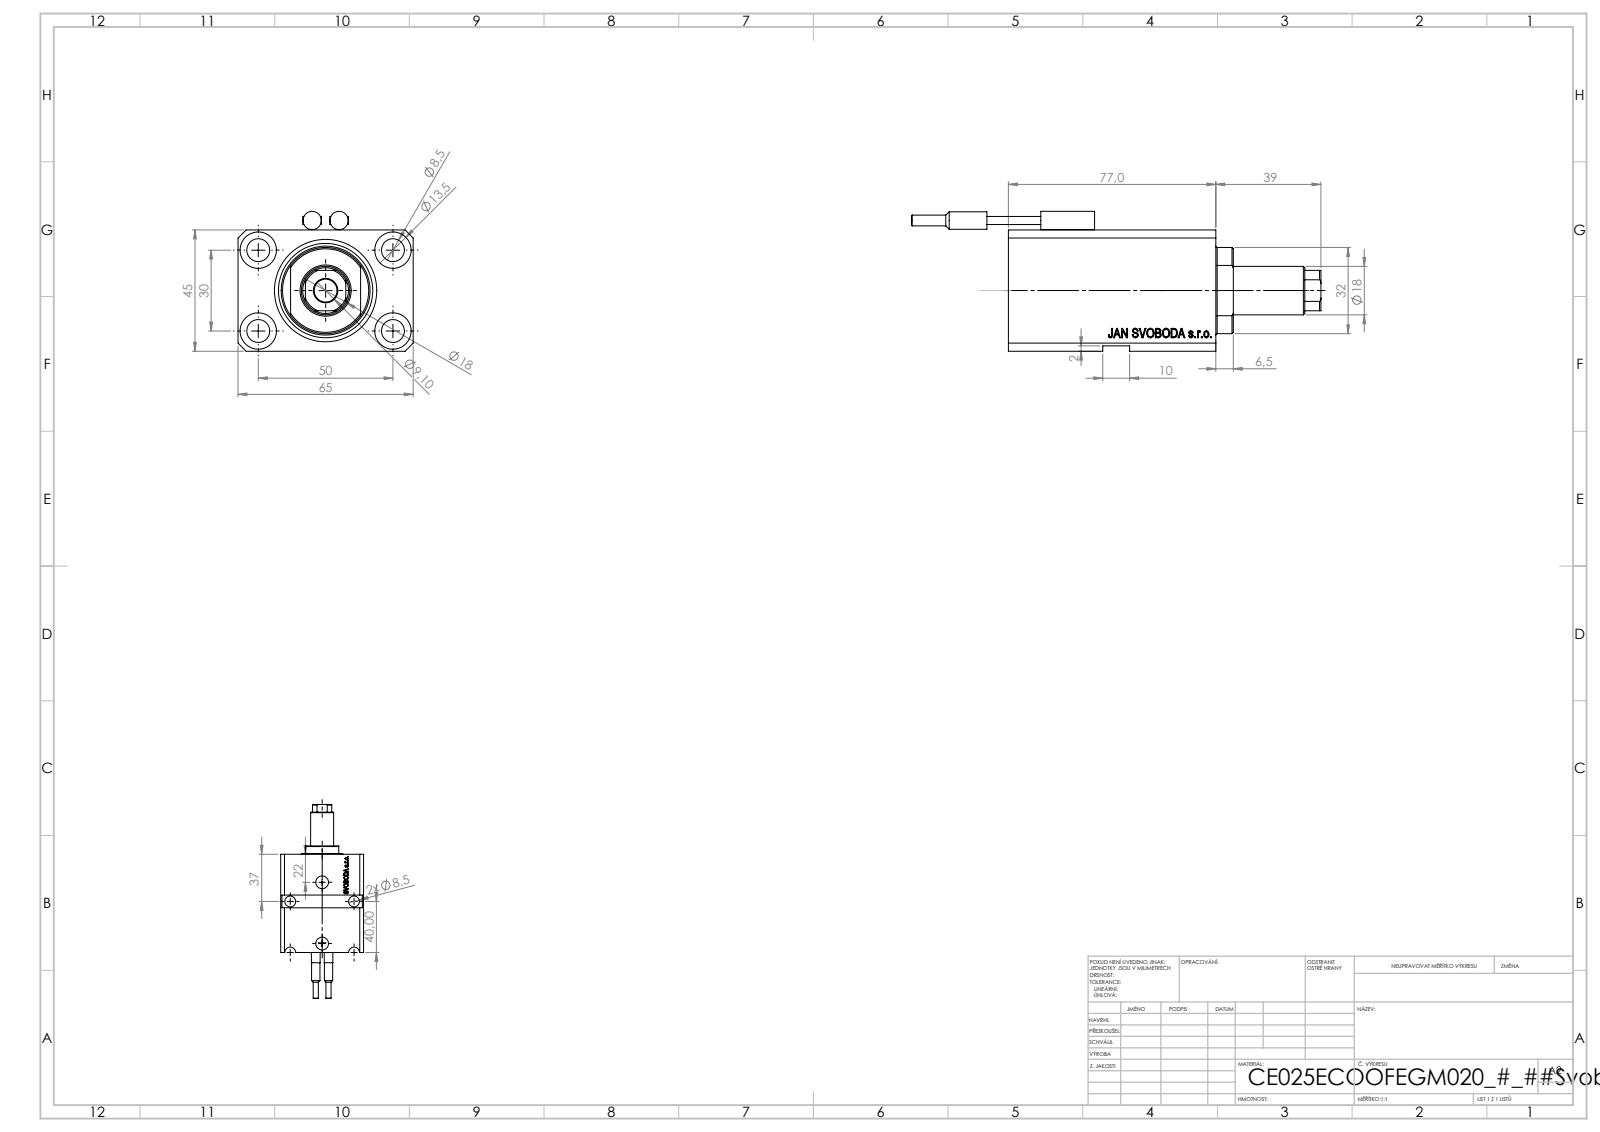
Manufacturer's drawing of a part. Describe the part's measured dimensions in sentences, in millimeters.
The part is named "V250CE_C_VCP; V250CE_VC_E; SWITCH_V250CE; V250CE_E_Body". Its 3-D file was written by "SolidWorks 2019 (CONFIG_CONTROL_DESIGN)". It is 5 solids with 942 faces: 466 planar, 90 cylindrical and 386 other. Overall it measures 152 by 65 by 51.9 millimeters. Its volume is 210 105 cubic millimeters and its surface area 53 901 square millimeters. Round holes: 7 of diameter 8.5, 4 of diameter 13.5, 2 of diameter 1.25, 2 of diameter 10, 1 of diameter 18, 1 of diameter 25, 1 of diameter 38. Round bosses or shafts: 2 of diameter 6.8, 2 of diameter 6.5, 2 of diameter 4. Partial cylindrical surfaces (rounded edges, fillets, slot ends): 2 of radius 4.25, 1 of radius 8.5, 1 of radius 16. The main face-to-face distances are 45, 65, 51.9, 77, 25.1, 32, 19.9, 2, 68, 9. The hole center spacings are 29.15, 50, 30, 40.98, 41.4, 58.31, 0.53, 47.47.
